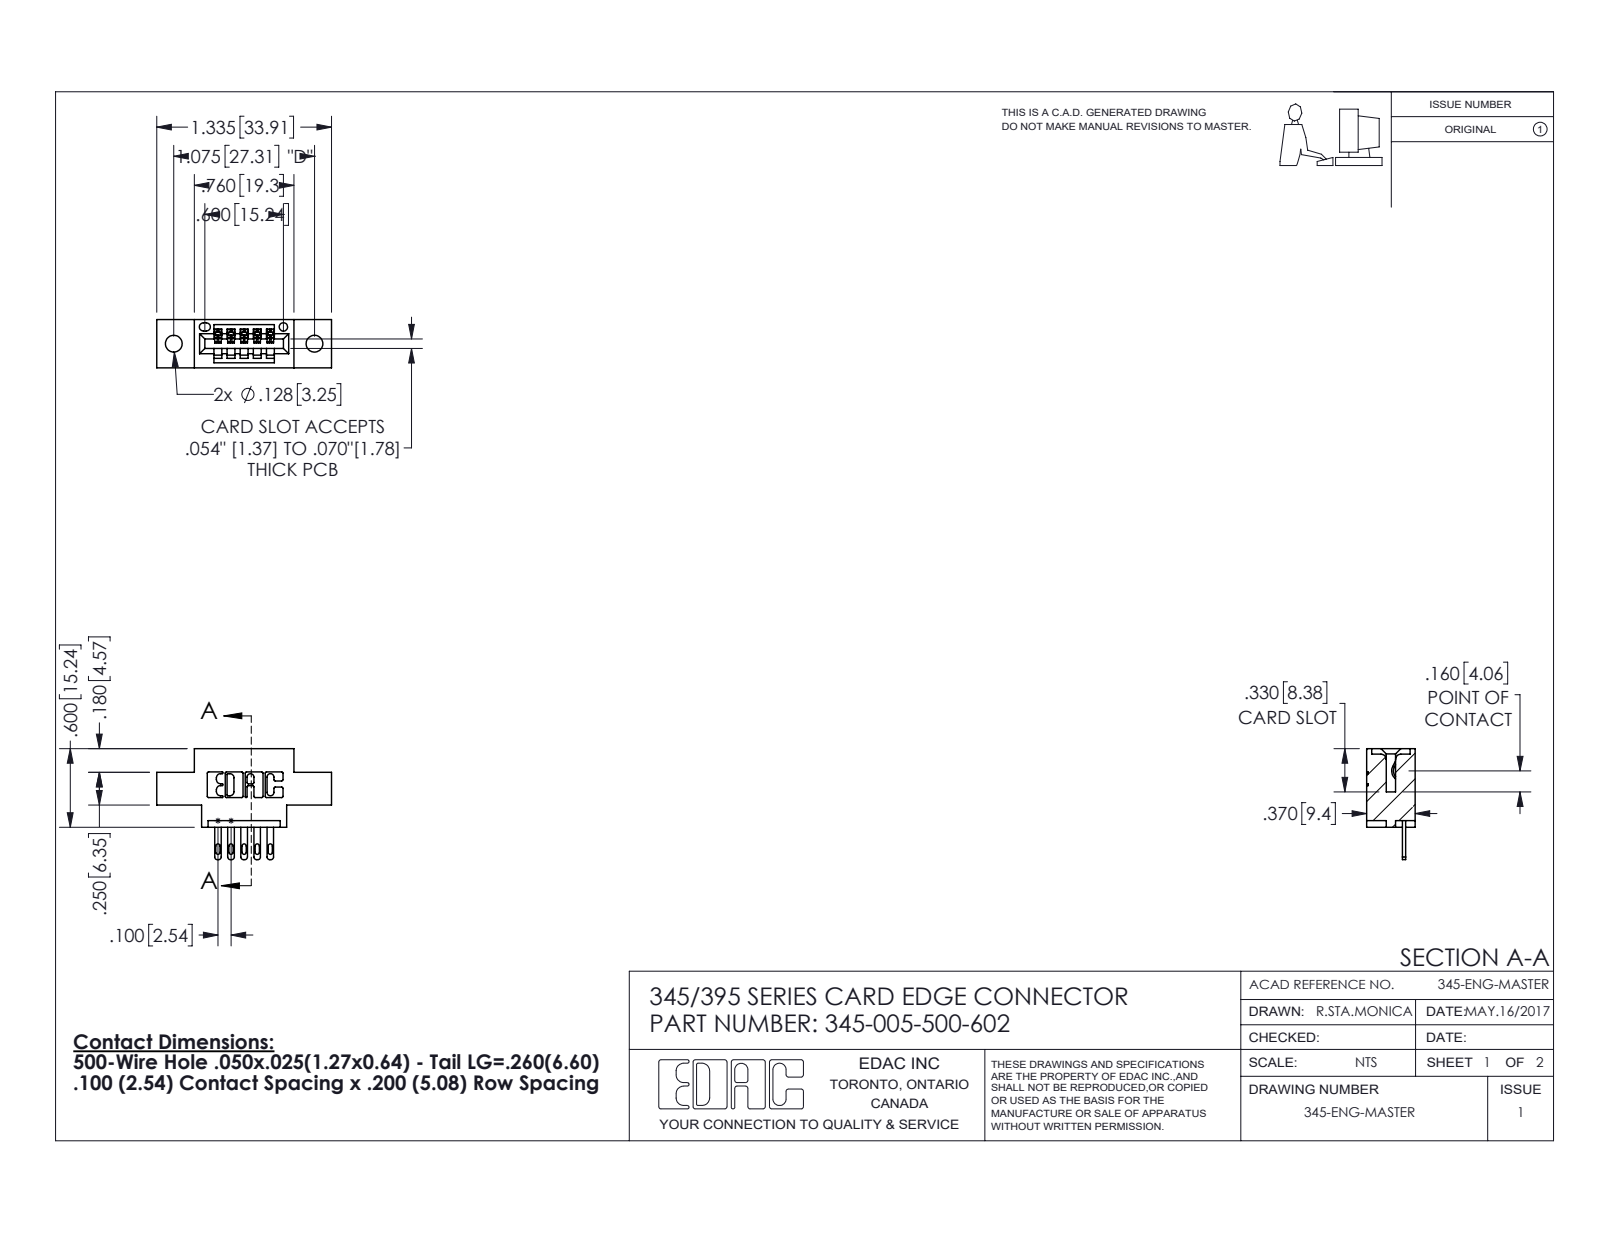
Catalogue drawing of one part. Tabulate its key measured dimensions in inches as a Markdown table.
| quantity | value |
| --- | --- |
| part name | 345-005-500-602; 345-292-001_345-293-100; 345 Part_0.170 Offset - 0.128 Dia |
| STEP written by | SolidWorks 2016 (CONFIG_CONTROL_DESIGN) |
| units | inches |
| bodies | 6 solids, 400 faces (254 planar, 146 cylindrical, 0 other) |
| overall size | 1.335 × 0.847 × 0.37 |
| volume | 0.169 in³ |
| surface area | 4.72 in² |
| round holes (diameter × count) | 0.128 × 2, 0.064 × 1 |
| partial cylindrical surfaces (radius × count) | 0.01 × 22, 0.006 × 10, 0.016 × 10, 0.02 × 10, 0.007 × 6, 0.031 × 6, 0.026 × 3, 0.031 × 2 |
| main face-to-face distances | 0.37, 0.2, 0.072, 0.298, 0.1, 0.025, 0.25, 0.098, 0.272, 0.06 |
| hole center spacings | 0.27, 0.847, 1.075 |
